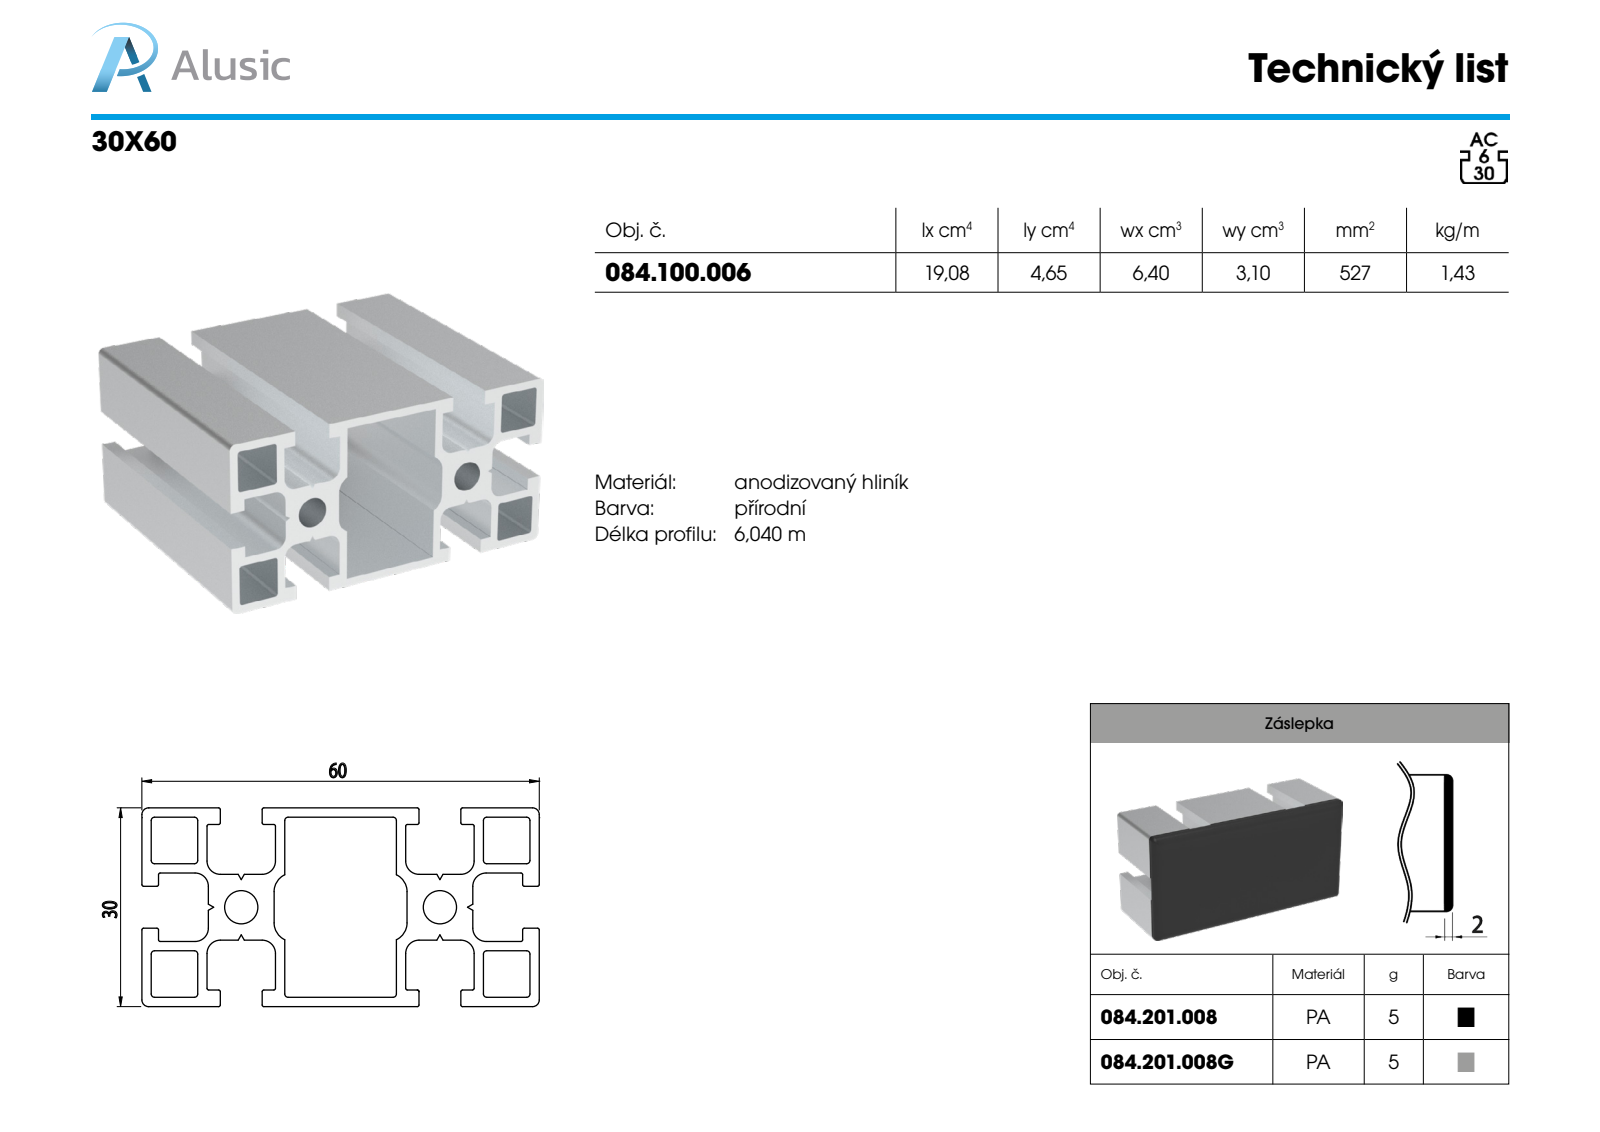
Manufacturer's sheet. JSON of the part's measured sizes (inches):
{"part_name": "084.201.008", "step_written_by": "SolidWorks 2011 (CONFIG_CONTROL_DESIGN)", "units": "inches", "bodies": {"solids": 1, "faces": 50, "planar": 14, "cylindrical": 24, "other": 12}, "overall_size": [2.362, 1.181, 0.413], "volume_in3": 0.305, "surface_area_in2": 8.021, "round_holes": [[0.217, 4]], "round_bosses_or_shafts": [[0.295, 4]], "partial_cylinders_radius": [[0.039, 4], [0.079, 4]], "face_to_face_distances": [0.098, 0.413, 0.315, 1.181, 2.362], "hole_center_spacings": [0.78, 1.961, 2.11]}
